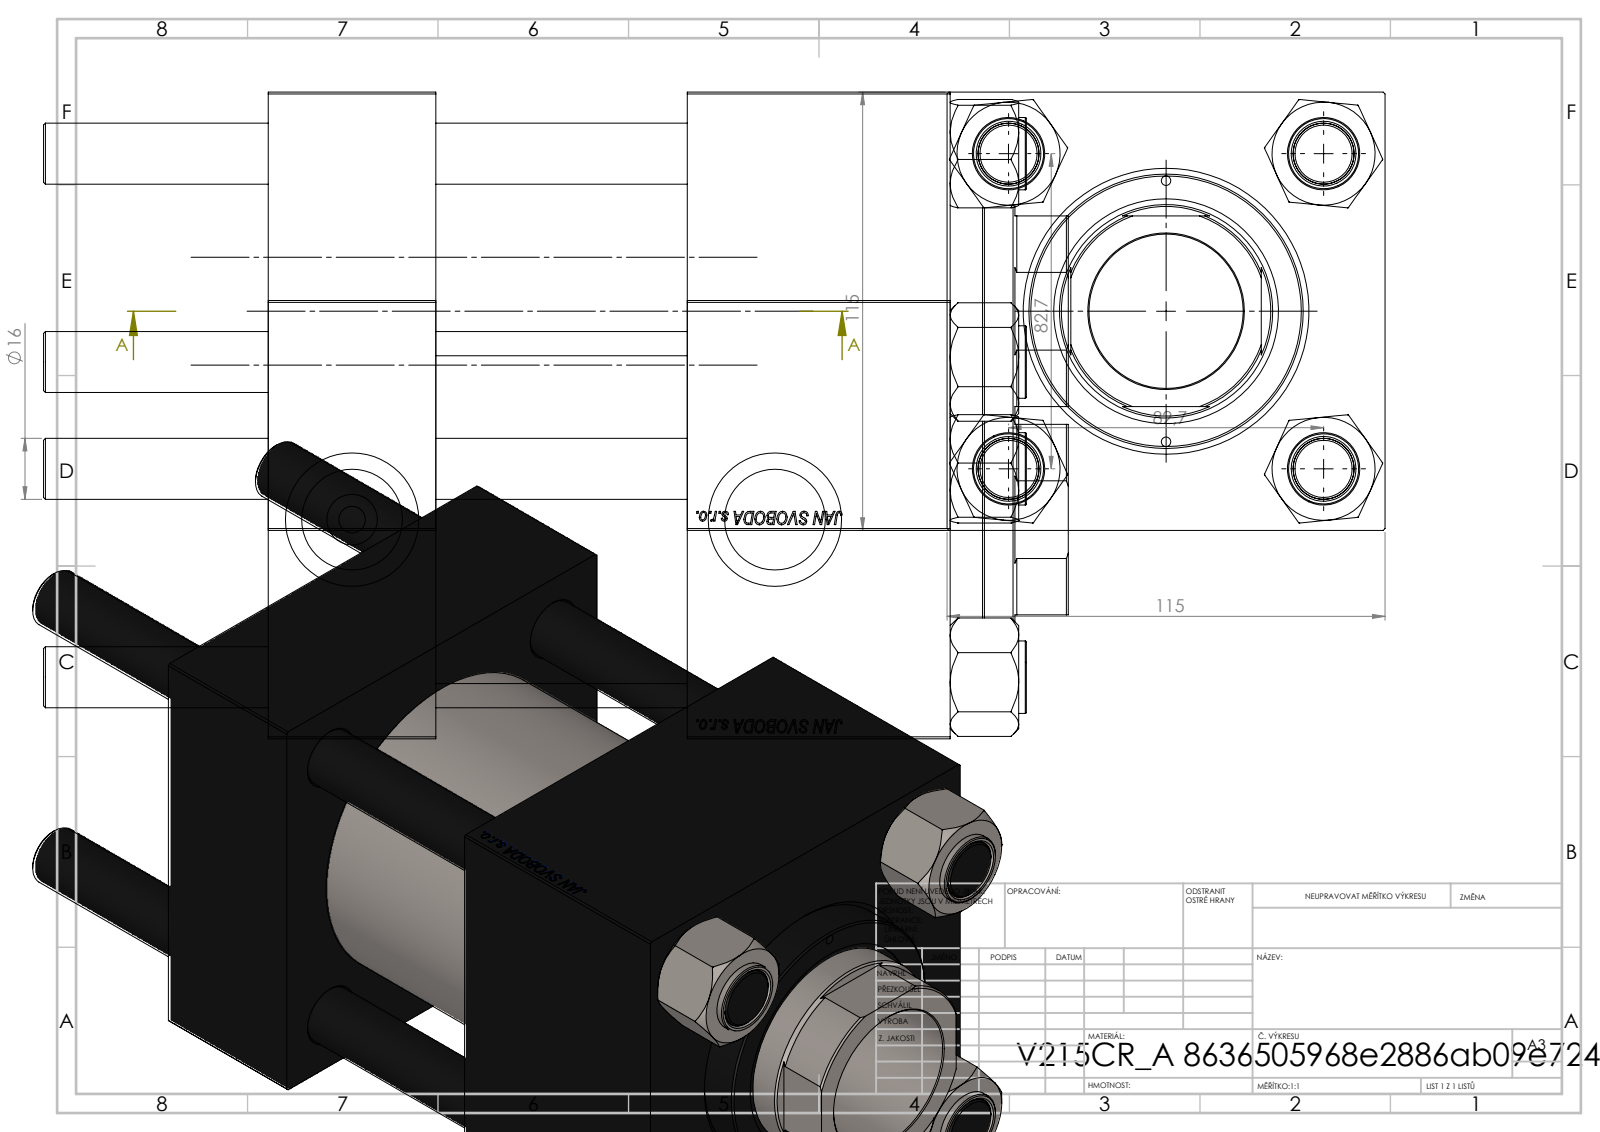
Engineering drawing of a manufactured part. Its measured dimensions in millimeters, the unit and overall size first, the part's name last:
Units: millimetres
Overall size (bounding box): 269 × 115 × 115
Round holes (diameter × count): ⌀16 ×4, ⌀2.5 ×2, ⌀7 ×2, ⌀26.44 ×2, ⌀35 ×2, ⌀40.5 ×1, ⌀56 ×1, ⌀59 ×1, ⌀61 ×1, ⌀72 ×1, ⌀80 ×1
Round bosses / shafts (diameter × count): ⌀19 ×4, ⌀86 ×1
Partial cylindrical surfaces — rounded edges, fillets, slot ends (radius × count): R27 ×1
Main face-to-face distances: 115, 44, 179, 135, 110, 66, 69, 20, 89, 150.3
Hole centre spacings: 41.96, 58.48, 82.7, 86.17, 34.25, 116.96, 68.5, 111
Volume: 1 941 000 mm³ · Surface area: 306 596 mm²
Bodies: 11 solids, 1185 faces (569 planar, 80 cylindrical, 536 other)
Part name (STEP PRODUCT): V215CR_BODY_A; NUT_M5; V215CR_VCP; CR025_012_A_0_G_A_G_M_020_+#_##_TYCINKA (+1 more)
STEP written by: SolidWorks 2019 (CONFIG_CONTROL_DESIGN)
